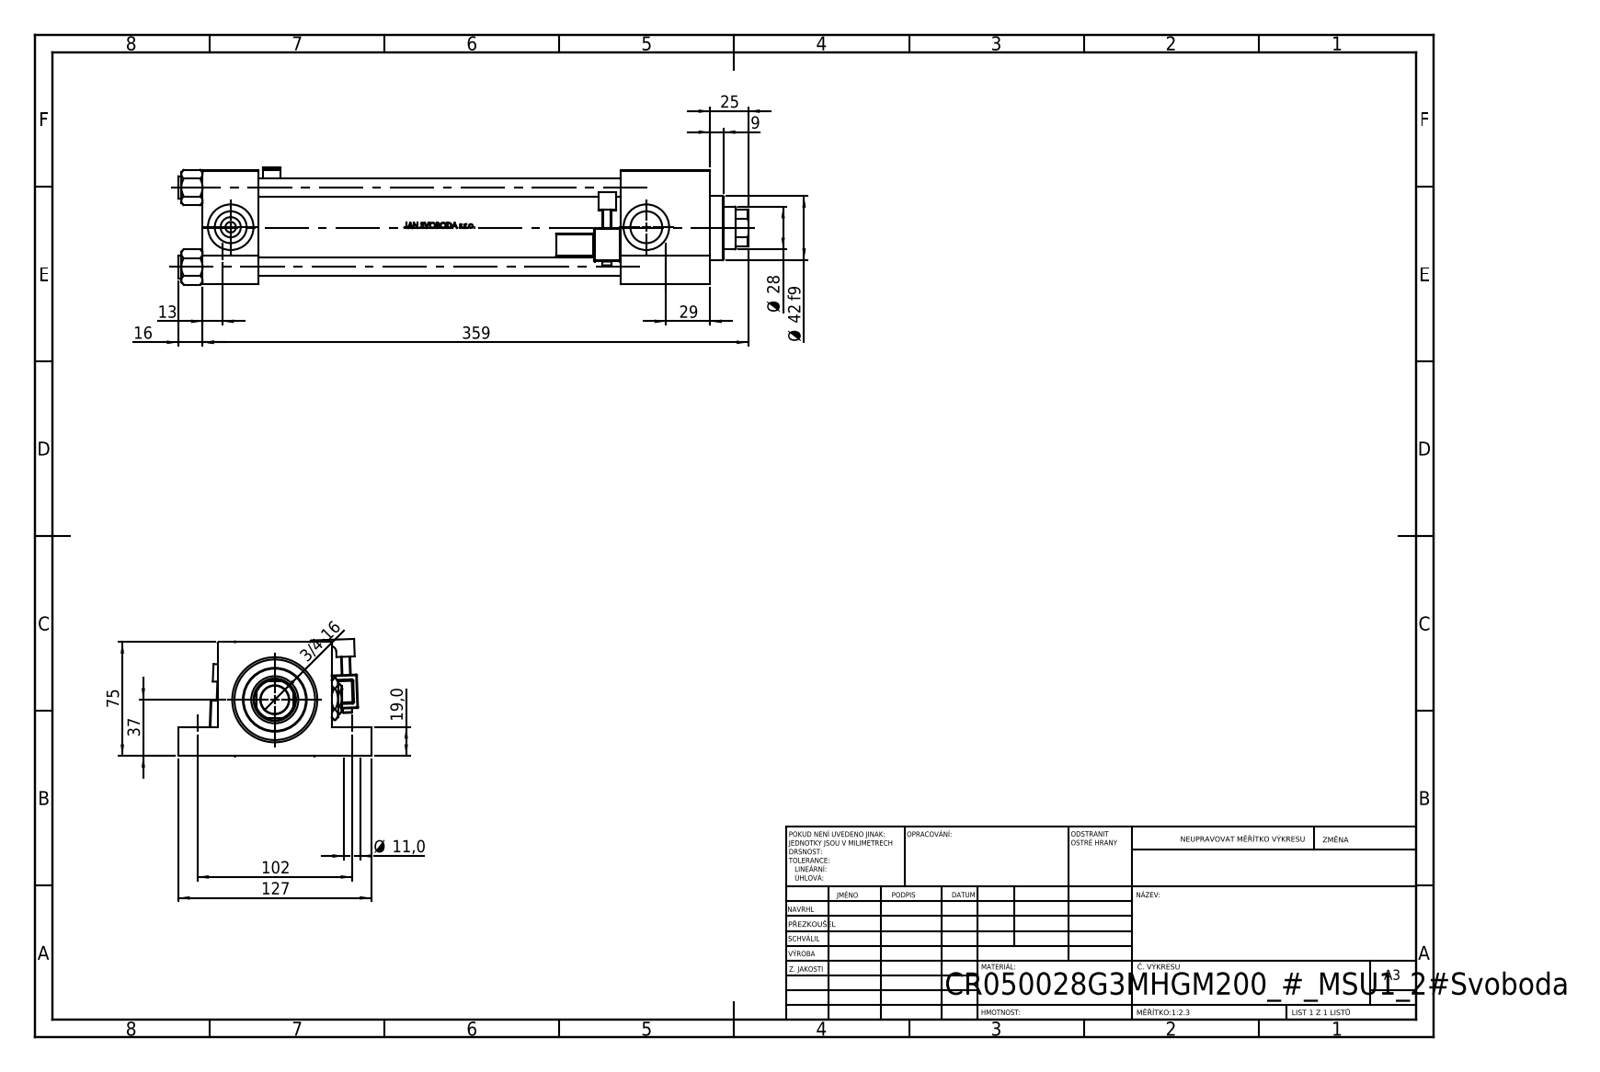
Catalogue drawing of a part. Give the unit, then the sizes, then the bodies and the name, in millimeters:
Units: millimetres
Overall size (bounding box): 375 × 127 × 77.3
Round holes (diameter × count): ⌀11 ×4, ⌀12 ×4, ⌀7 ×2, ⌀20.96 ×2, ⌀30 ×2, ⌀18.5 ×1, ⌀28 ×1, ⌀31 ×1, ⌀41 ×1, ⌀50 ×1, ⌀53 ×1
Round bosses / shafts (diameter × count): ⌀15 ×4, ⌀6 ×2, ⌀56 ×1, ⌀42 ×1
Partial cylindrical surfaces — rounded edges, fillets, slot ends (radius × count): R0.5 ×48, R1 ×2, R2.5 ×2, R4 ×2, R6 ×1, R13.5 ×1
Main face-to-face distances: 75, 37, 334, 297, 56, 19, 275, 238, 59, 26
Hole centre spacings: 52.3, 36.63, 37.34, 73.96, 102, 292, 309.3, 273.5
Volume: 1 086 000 mm³ · Surface area: 282 750 mm²
Bodies: 15 solids, 1337 faces (535 planar, 192 cylindrical, 610 other)
Part name (STEP PRODUCT): V215_VC_A; V215CR_G_TYCINKA; Zatka_pro_OIL_PORT; V215CR_VCP_G (+3 more)
STEP written by: SolidWorks 2019 (CONFIG_CONTROL_DESIGN)
